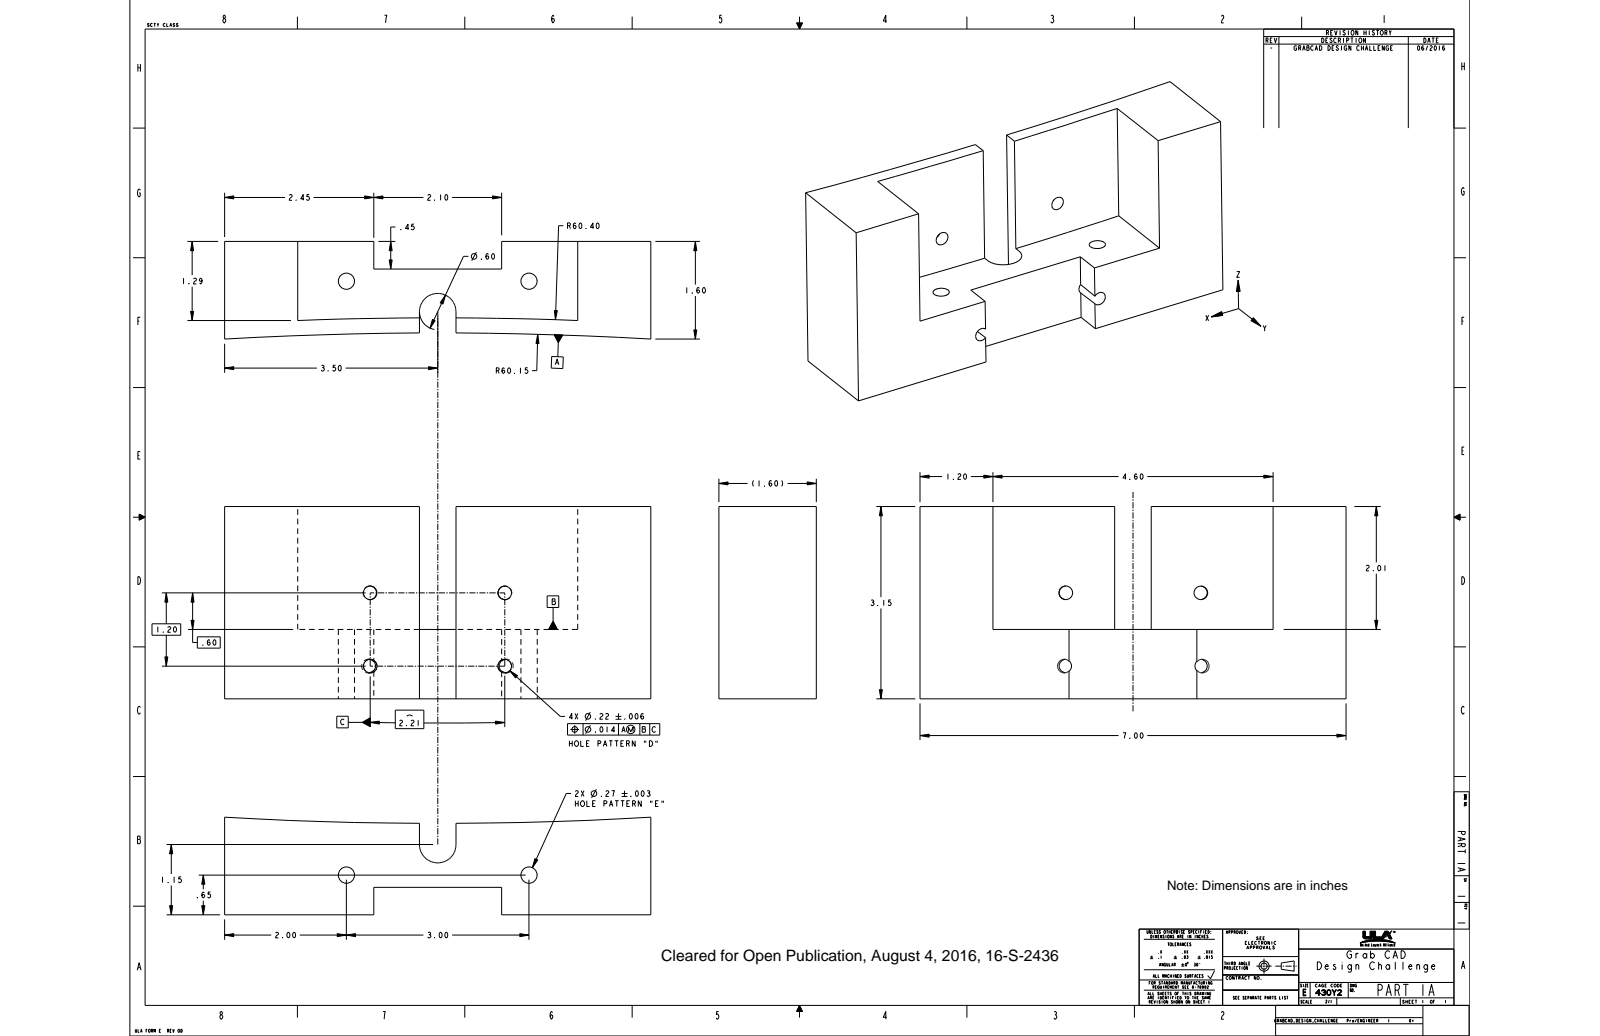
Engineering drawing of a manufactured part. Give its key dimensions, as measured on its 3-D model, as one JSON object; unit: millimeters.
{"part_name": "Cabinet; Drawer front plate; Cabinet drawer development", "step_written_by": "Autodesk Inventor 2015 (AUTOMOTIVE_DESIGN)", "units": "millimeters", "bodies": {"solids": 5, "faces": 393, "planar": 150, "cylindrical": 155, "other": 88}, "overall_size": [1996, 657.5, 430], "volume_mm3": 101200000, "surface_area_mm2": 12620000, "partial_cylinders_radius": [[1, 106], [8, 1]], "face_to_face_distances": [16, 414, 430, 140, 398, 657.5, 15, 642.5, 220, 124]}
